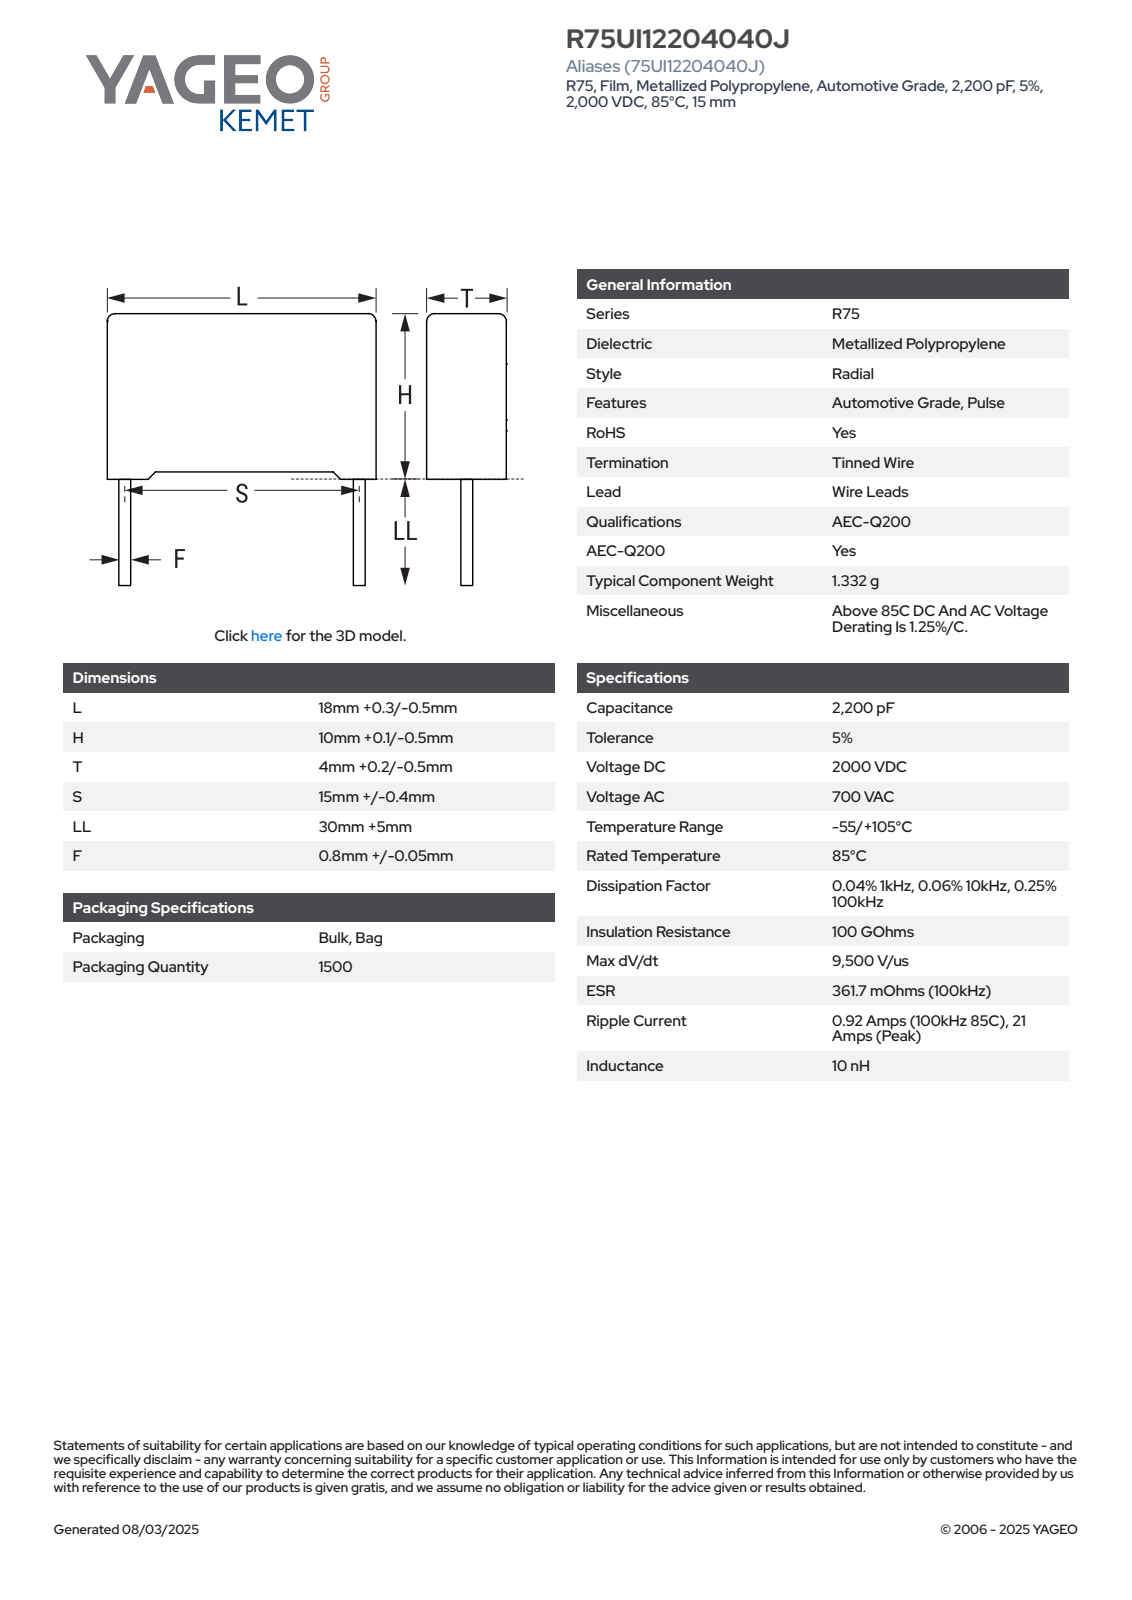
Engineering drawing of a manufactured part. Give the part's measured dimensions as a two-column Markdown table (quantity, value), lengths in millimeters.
| quantity | value |
| --- | --- |
| part name | CFR_RB2_18X10X4_L18.3H10.1T4.2S15LL35F0.85 |
| STEP written by | SolidWorks 2021 (AUTOMOTIVE_DESIGN) |
| units | millimeters |
| bodies | 4 solids, 85 faces (77 planar, 8 cylindrical, 0 other) |
| overall size | 45.1 × 18.3 × 4.21 |
| volume | 771 mm³ |
| surface area | 829 mm² |
| round bosses / shafts (diameter × count) | 0.85 × 2 |
| partial cylindrical surfaces (radius × count) | 0.5 × 4 |
| main face-to-face distances | 4.2, 9.35, 18.3, 0.61, 3.59, 0.4, 9.75, 0.75, 0.35, 10.1 |
